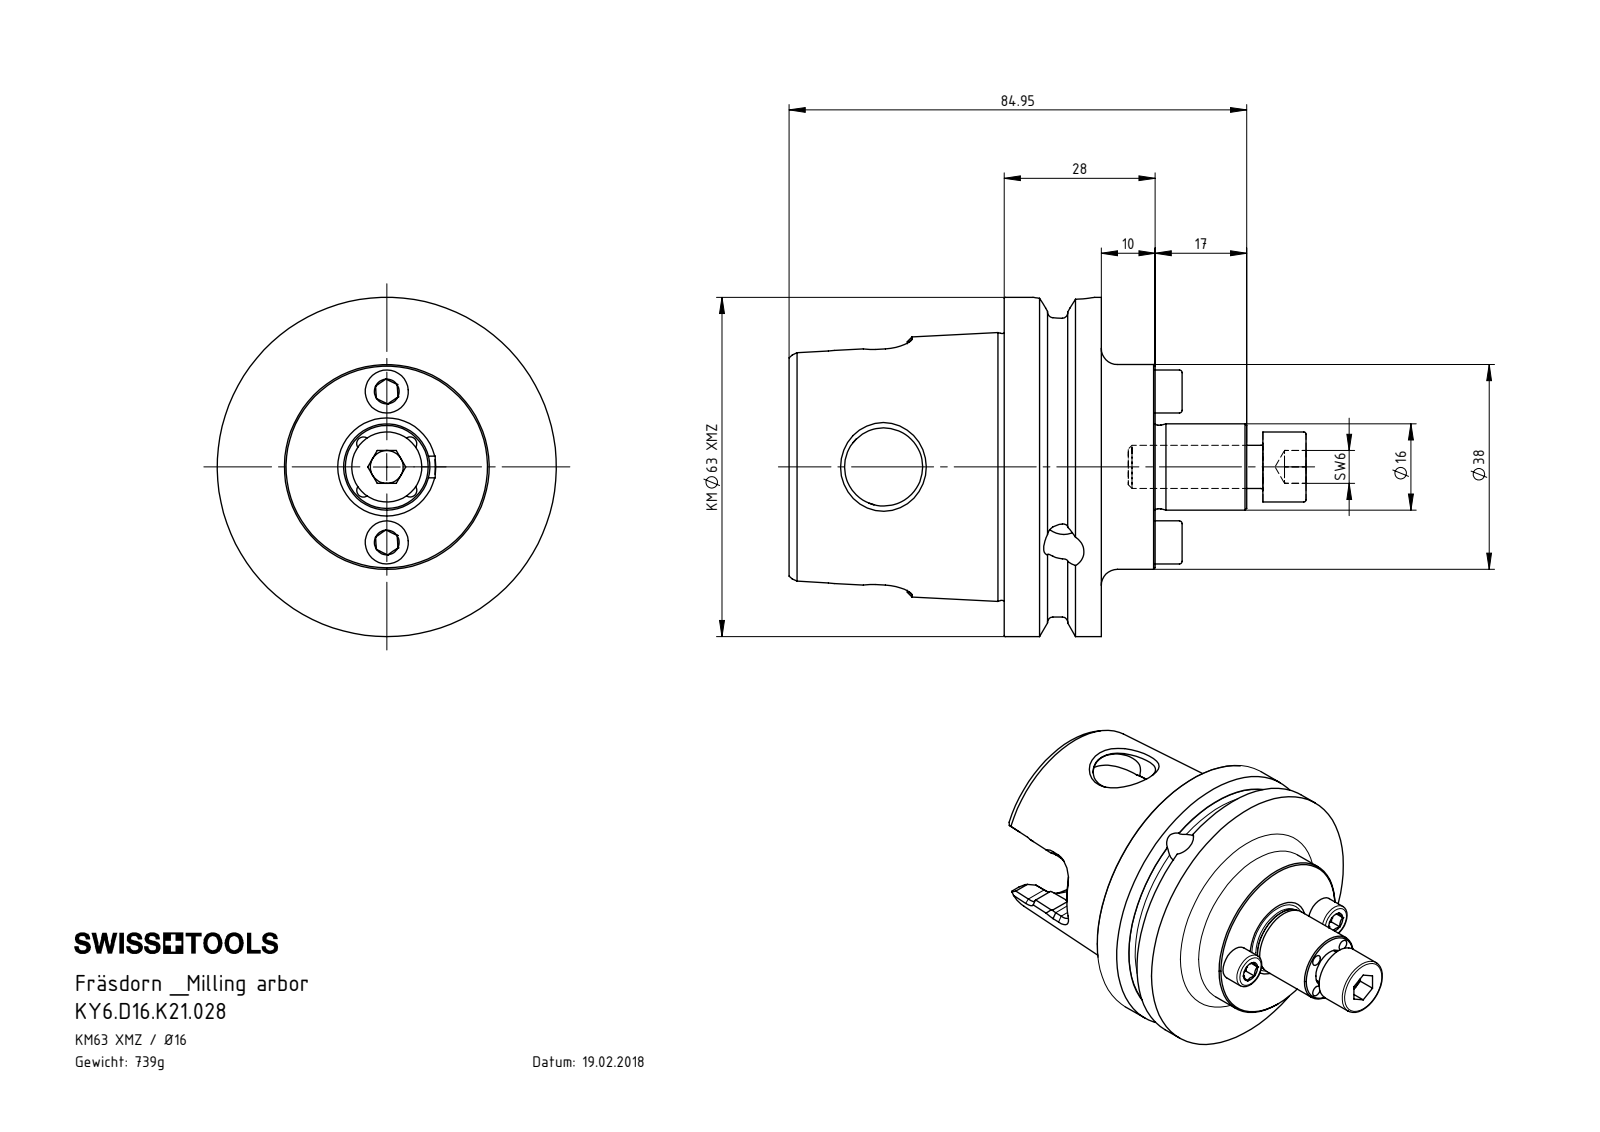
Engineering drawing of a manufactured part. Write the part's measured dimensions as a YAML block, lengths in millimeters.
part_name: "D16-ER1.002.025_A; D16-ER2.001.015_B; KY6.D16.K21.028; KY6-D16.K21.028_A"
step_written_by: "SolidWorks 2017 (CONFIG_CONTROL_DESIGN)"
units: millimeters
bodies: {solids: 4, faces: 392, planar: 87, cylindrical: 100, other: 205}
overall_size: [95.95, 62.95, 62.95]
volume: 94293
surface_area: 25602
round_holes:
  - {diameter: 2.5, count: 3}
  - {diameter: 3.3, count: 2}
  - {diameter: 6, count: 2}
  - {diameter: 7.47, count: 2}
  - {diameter: 6.8, count: 1}
  - {diameter: 8.48, count: 1}
  - {diameter: 8.5, count: 1}
  - {diameter: 10, count: 1}
  - {diameter: 11.5, count: 1}
  - {diameter: 14.5, count: 1}
  - {diameter: 31.1, count: 1}
  - {diameter: 35.27, count: 1}
round_bosses_or_shafts:
  - {diameter: 8, count: 3}
  - {diameter: 4, count: 2}
  - {diameter: 3, count: 2}
  - {diameter: 62.95, count: 1}
  - {diameter: 55.7, count: 1}
  - {diameter: 38, count: 1}
  - {diameter: 16, count: 1}
  - {diameter: 15.5, count: 1}
partial_cylinders:
  - {radius: 4, count: 6}
  - {radius: 2, count: 2}
  - {radius: 7.04, count: 2}
face_to_face_distances: [18, 28, 10, 19.1, 1.1, 29.1, 24, 6, 34, 4.9]
hole_center_spacings: [6.12, 10.6, 14, 18.83, 12.25, 28]
